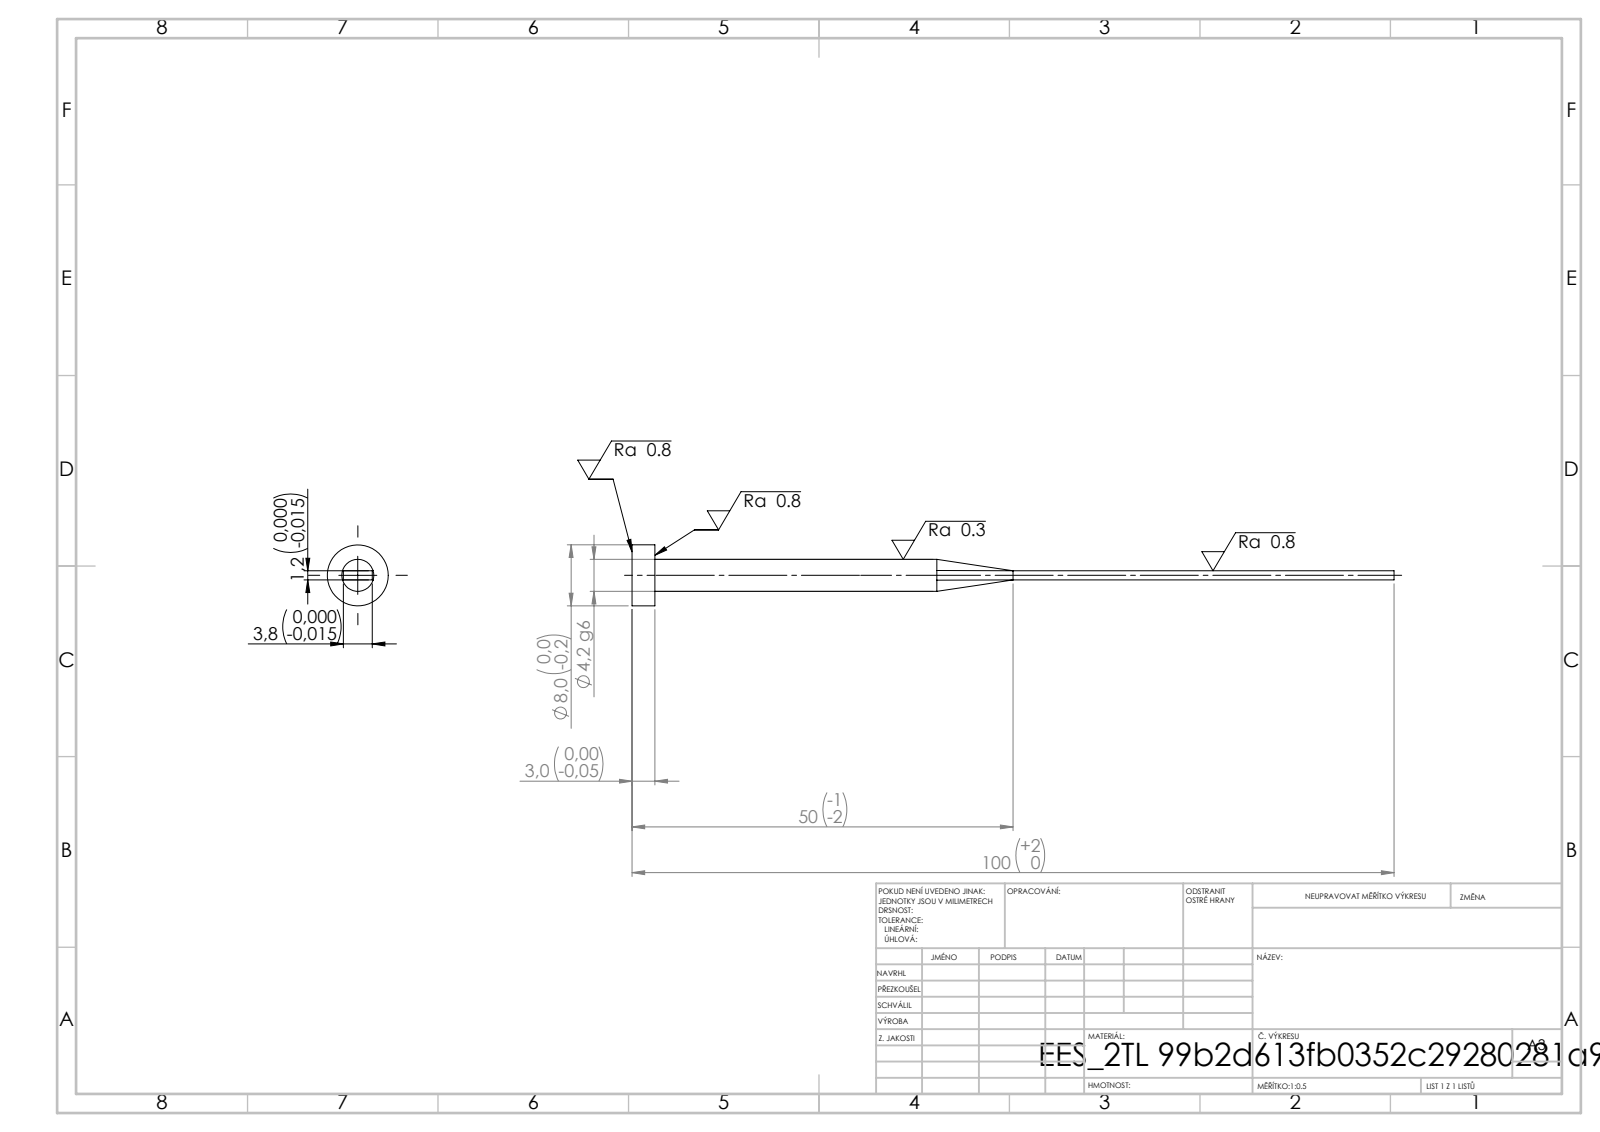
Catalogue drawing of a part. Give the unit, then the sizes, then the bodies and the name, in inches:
Units: inches
Overall size (bounding box): 3.937 × 0.315 × 0.315
Round bosses / shafts (diameter × count): ⌀0.315 ×1, ⌀0.165 ×1
Main face-to-face distances: 0.047, 0.15, 0.118, 3.937, 3.819
Volume: 0.06 in³ · Surface area: 1.964 in²
Bodies: 1 solid, 15 faces (7 planar, 4 cylindrical, 4 other)
STEP written by: SolidWorks 2019 (CONFIG_CONTROL_DESIGN)
